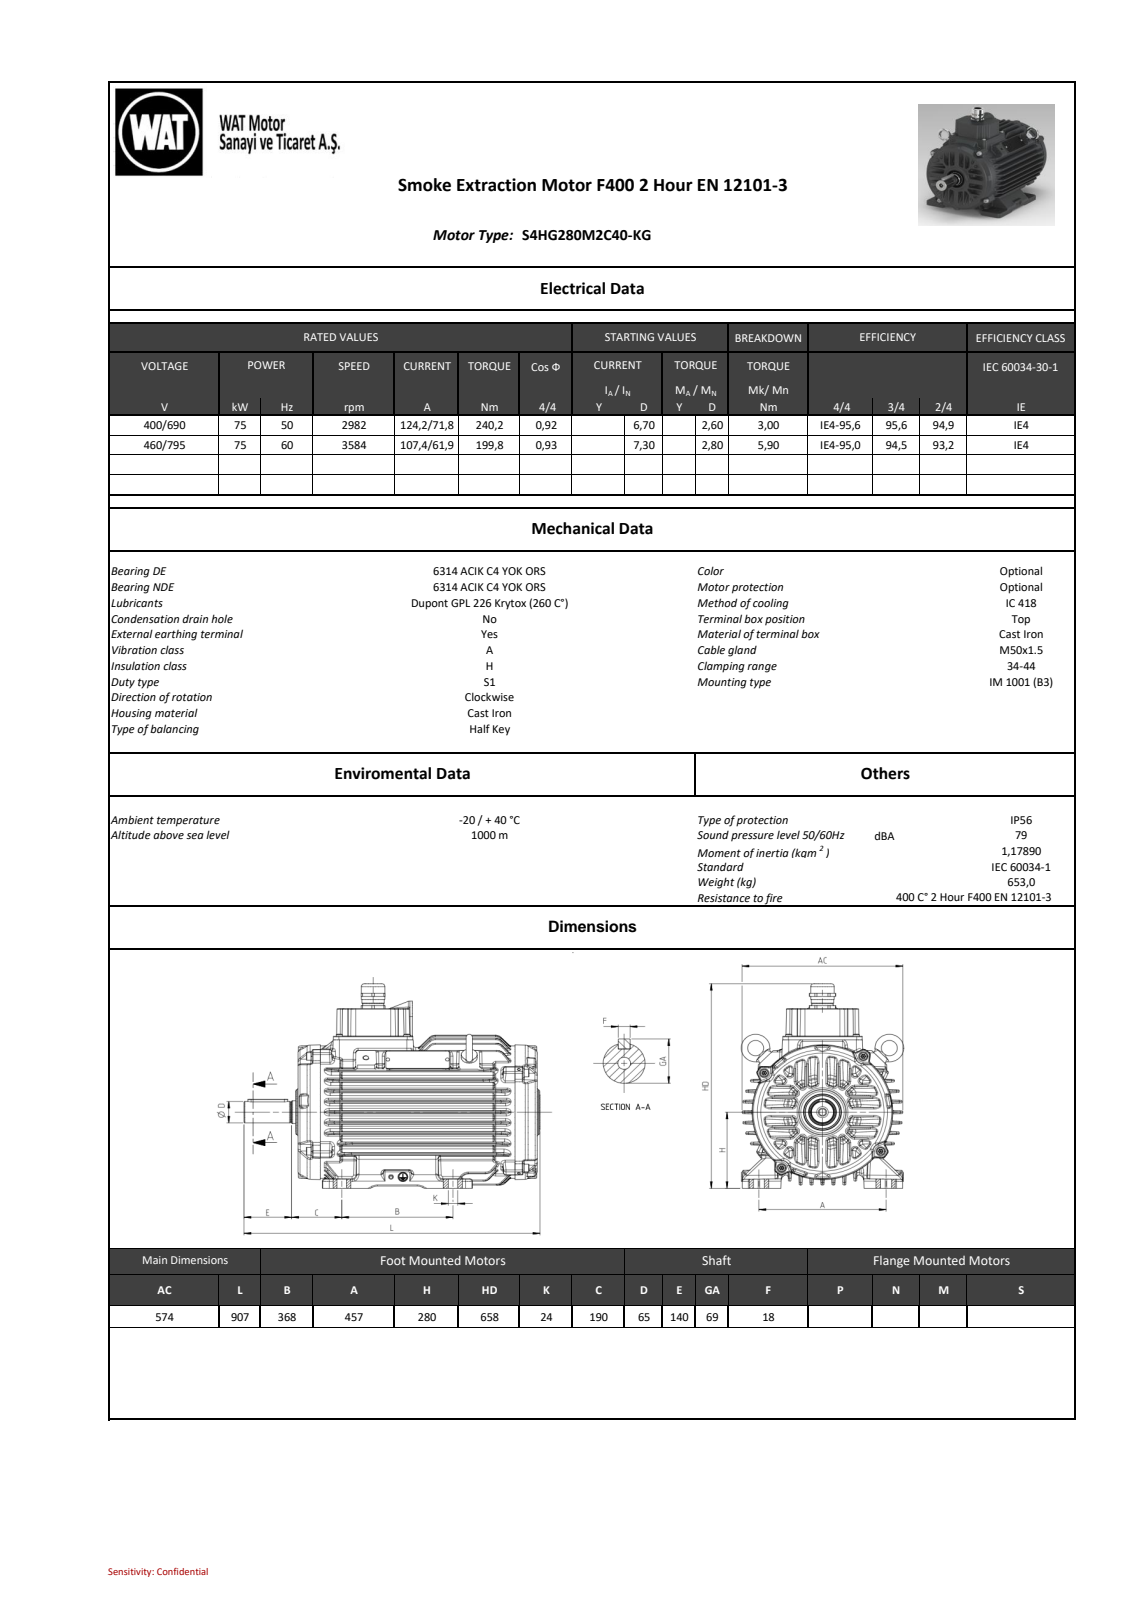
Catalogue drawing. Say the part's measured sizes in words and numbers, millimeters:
The part is named "AA_objects". Its 3-D file was written by "SIEMENS PLM Software NX2206.8101 (AP203_CONFIGURATION_CONTROLLED_3D_DESIGN_OF_MECHANICAL_PARTS_AND_ASSEMBLIES_MIM_LF)". It is 0 solids with 3703 faces: 671 planar, 1078 cylindrical and 1954 other. Overall it measures 906.83 by 657.86 by 573.9 millimeters. Round holes: 9 of diameter 7.2, 5 of diameter 21, 4 of diameter 14.75, 2 of diameter 4.5, 2 of diameter 12, 2 of diameter 18.5, 1 of diameter 2.5, 1 of diameter 44, 1 of diameter 72, 1 of diameter 82.31. Round bosses or shafts: 4 of diameter 27.4, 4 of diameter 23.67, 4 of diameter 18.1, 4 of diameter 15.73, 2 of diameter 40, 2 of diameter 8, 1 of diameter 520, 1 of diameter 80. Partial cylindrical surfaces (rounded edges, fillets, slot ends): 291 of radius 1.5, 87 of radius 2, 71 of radius 3, 42 of radius 5, 23 of radius 4, 17 of radius 8, 12 of radius 12, 12 of radius 22. The main face-to-face distances are 27.62, 55.24, 55.79, 31.52, 221.79, 13.5, 27.9, 27.89, 82.86, 27.56. The hole center spacings are 109.66, 228.07, 273.49, 328.78, 386.78, 576.13, 72.5, 110.44.
